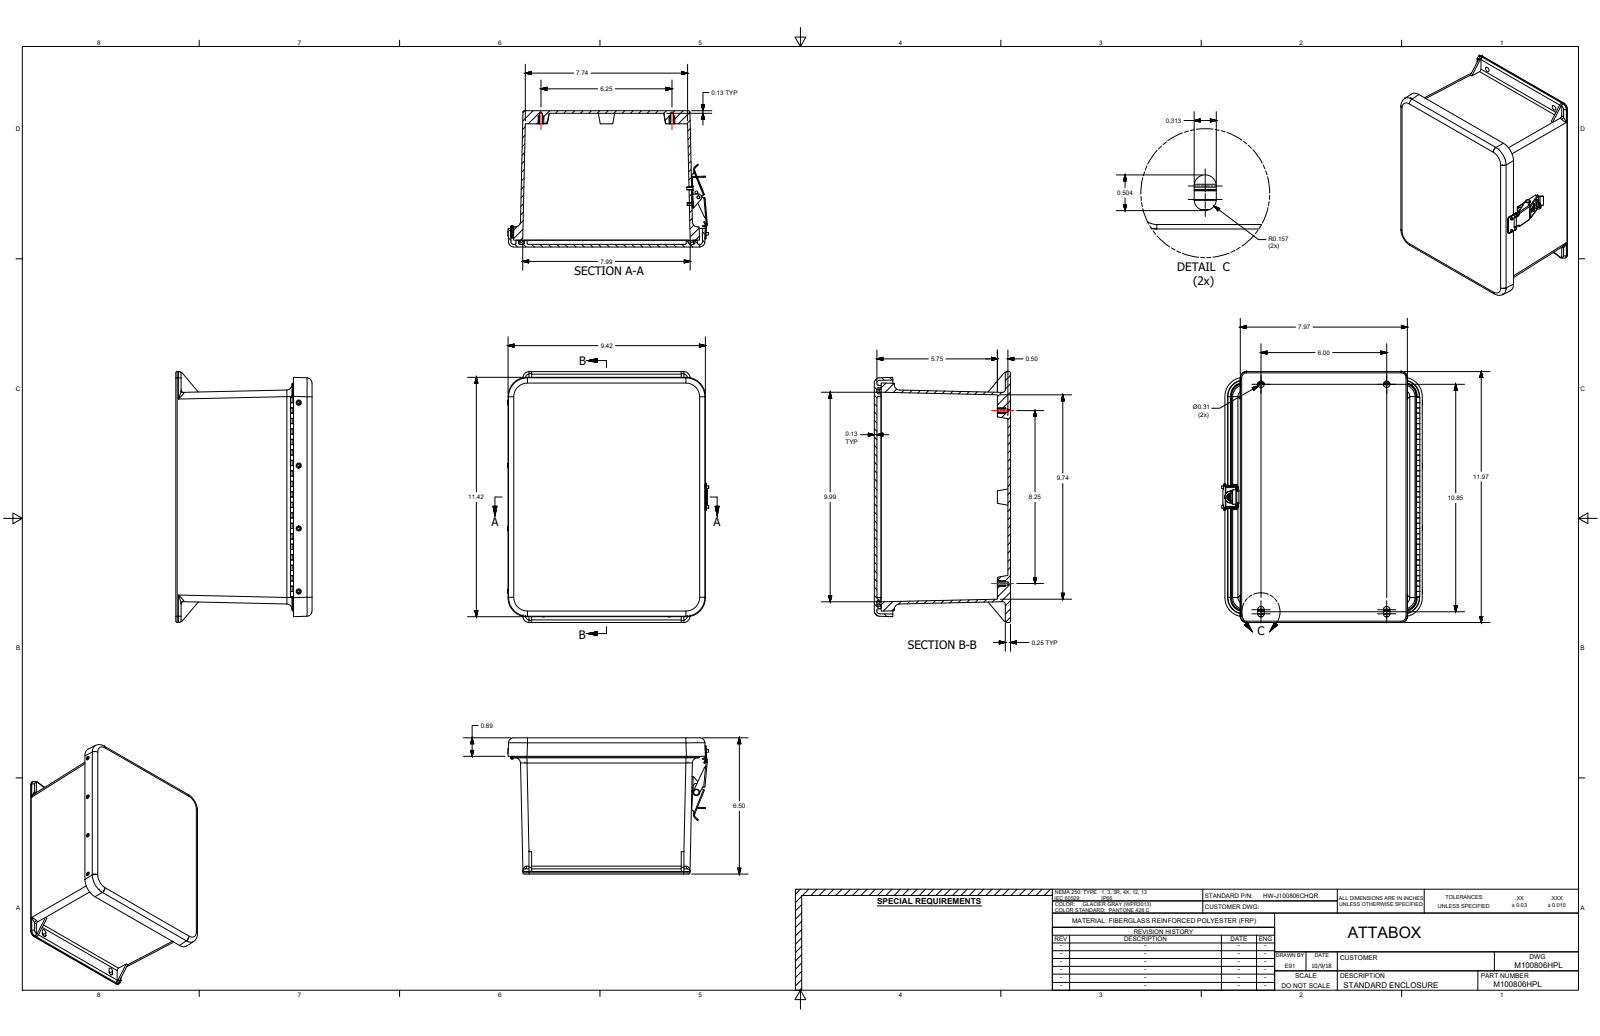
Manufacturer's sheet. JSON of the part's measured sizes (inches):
{"part_name": "M100806HPL", "step_written_by": "SolidWorks 2018 (AUTOMOTIVE_DESIGN)", "units": "inches", "bodies": {"solids": 36, "faces": 1172, "planar": 450, "cylindrical": 454, "other": 268}, "overall_size": [11.966, 9.846, 6.499], "volume_in3": 76.62, "surface_area_in2": 1030, "round_holes": [[0.14, 14], [0.104, 12], [0.152, 12], [0.159, 12], [0.131, 8], [0.375, 5], [0.13, 2], [0.135, 2], [0.313, 2], [0.085, 1], [0.135, 1]], "round_bosses_or_shafts": [[0.27, 12], [0.125, 7], [0.125, 5], [0.3, 1], [0.17, 1], [0.155, 1], [0.155, 1], [0.12, 1]], "partial_cylinders_radius": [[0.031, 26], [0.125, 22], [0.063, 21], [0.063, 20], [0.039, 16], [0.062, 13], [0.015, 12], [0.3, 12]], "face_to_face_distances": [0.125, 6.499, 0.122, 0.123, 6.374, 6.249, 0.125, 6.374, 6.172, 6.047], "hole_center_spacings": [6, 3, 2.5, 0.938, 3.5, 8.5, 9, 0.75]}
